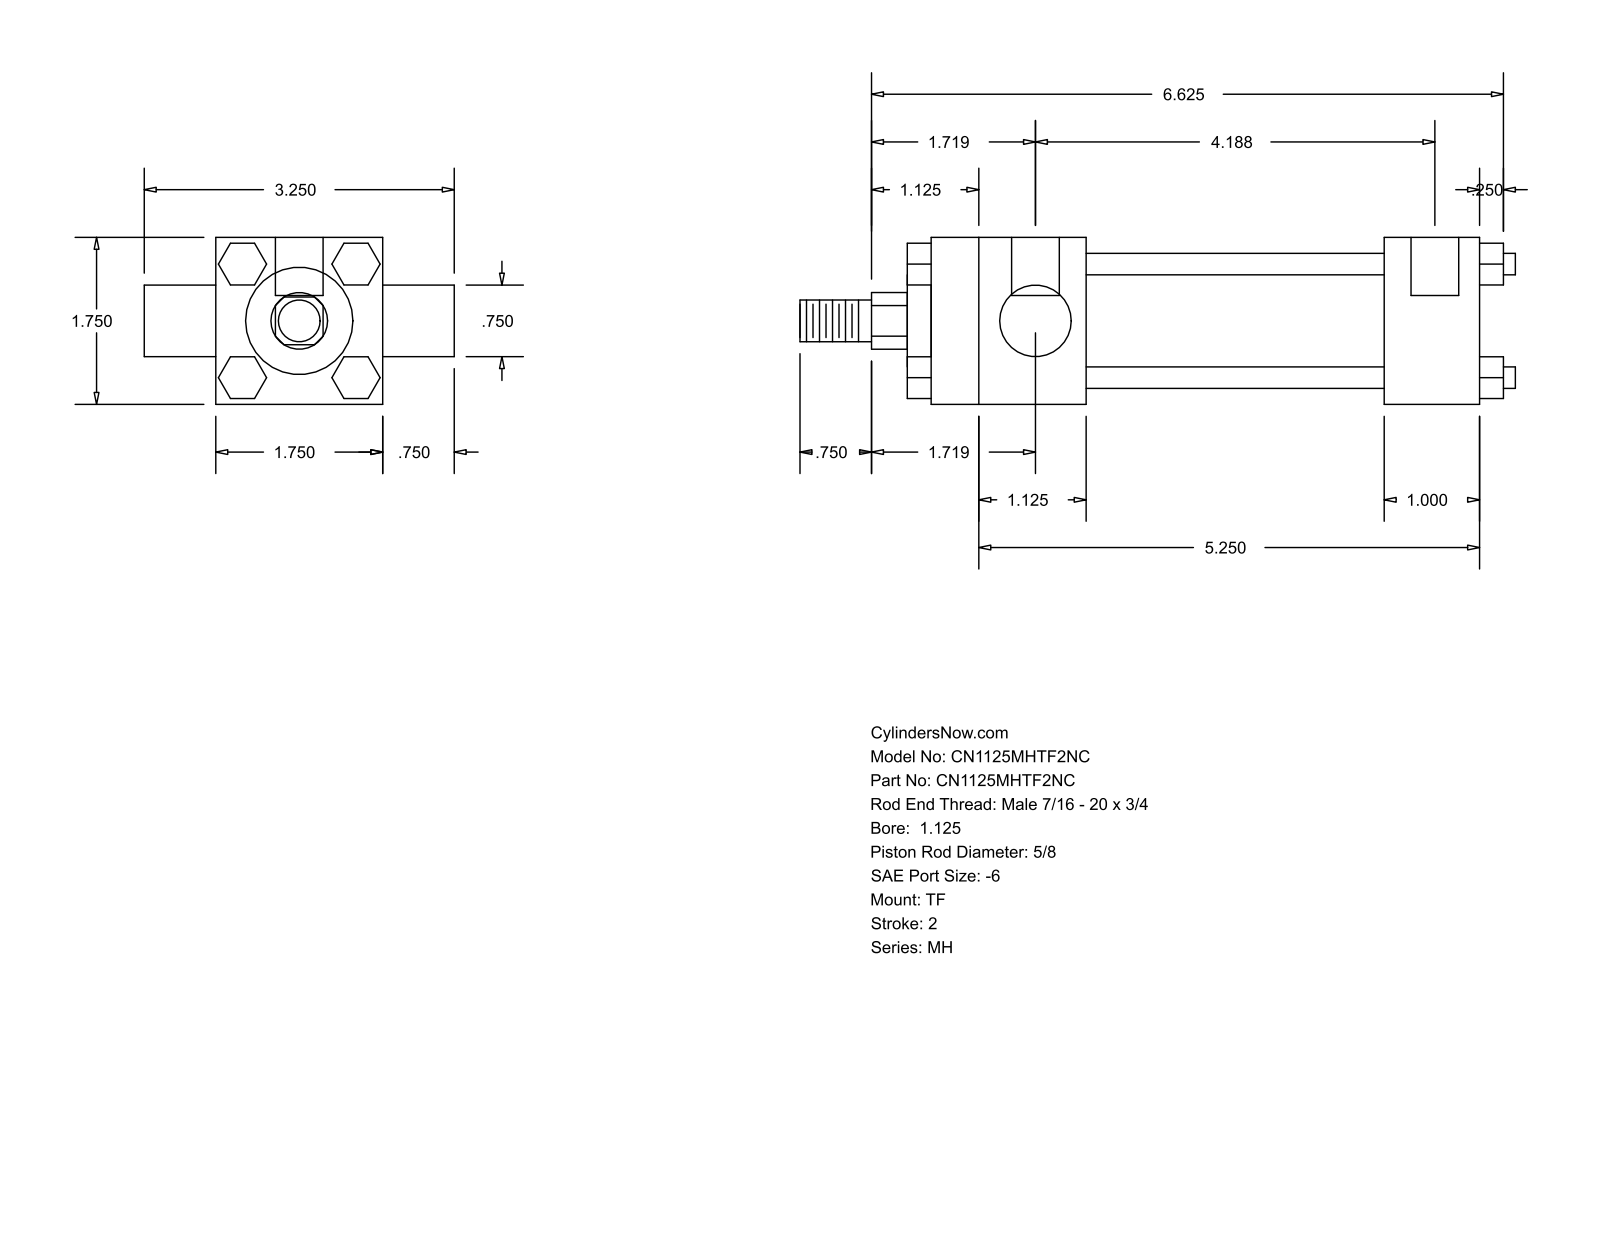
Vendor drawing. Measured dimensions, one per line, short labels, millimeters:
name: MH_TF__0112_0.625
written by: GSSL Pune (CONFIG_CONTROL_DESIGN)
unit: mm
bodies: 0 solids, 120 faces (92 planar, 28 cylindrical, 0 other)
size: 190.5 × 82.55 × 44.45
holes: 3× ⌀5.56, 2× ⌀12.7
bosses: 4× ⌀5.71, 1× ⌀34.92, 1× ⌀28.57, 1× ⌀19.05, 1× ⌀15.88, 1× ⌀11.11
rounds: 1× R7.54
face distances: 44.46, 6.35, 152.4, 11.11, 25.4, 79.38, 104.78, 41.27, 120.65, 146.05
hole spacings: 3.17, 103.19, 106.36
